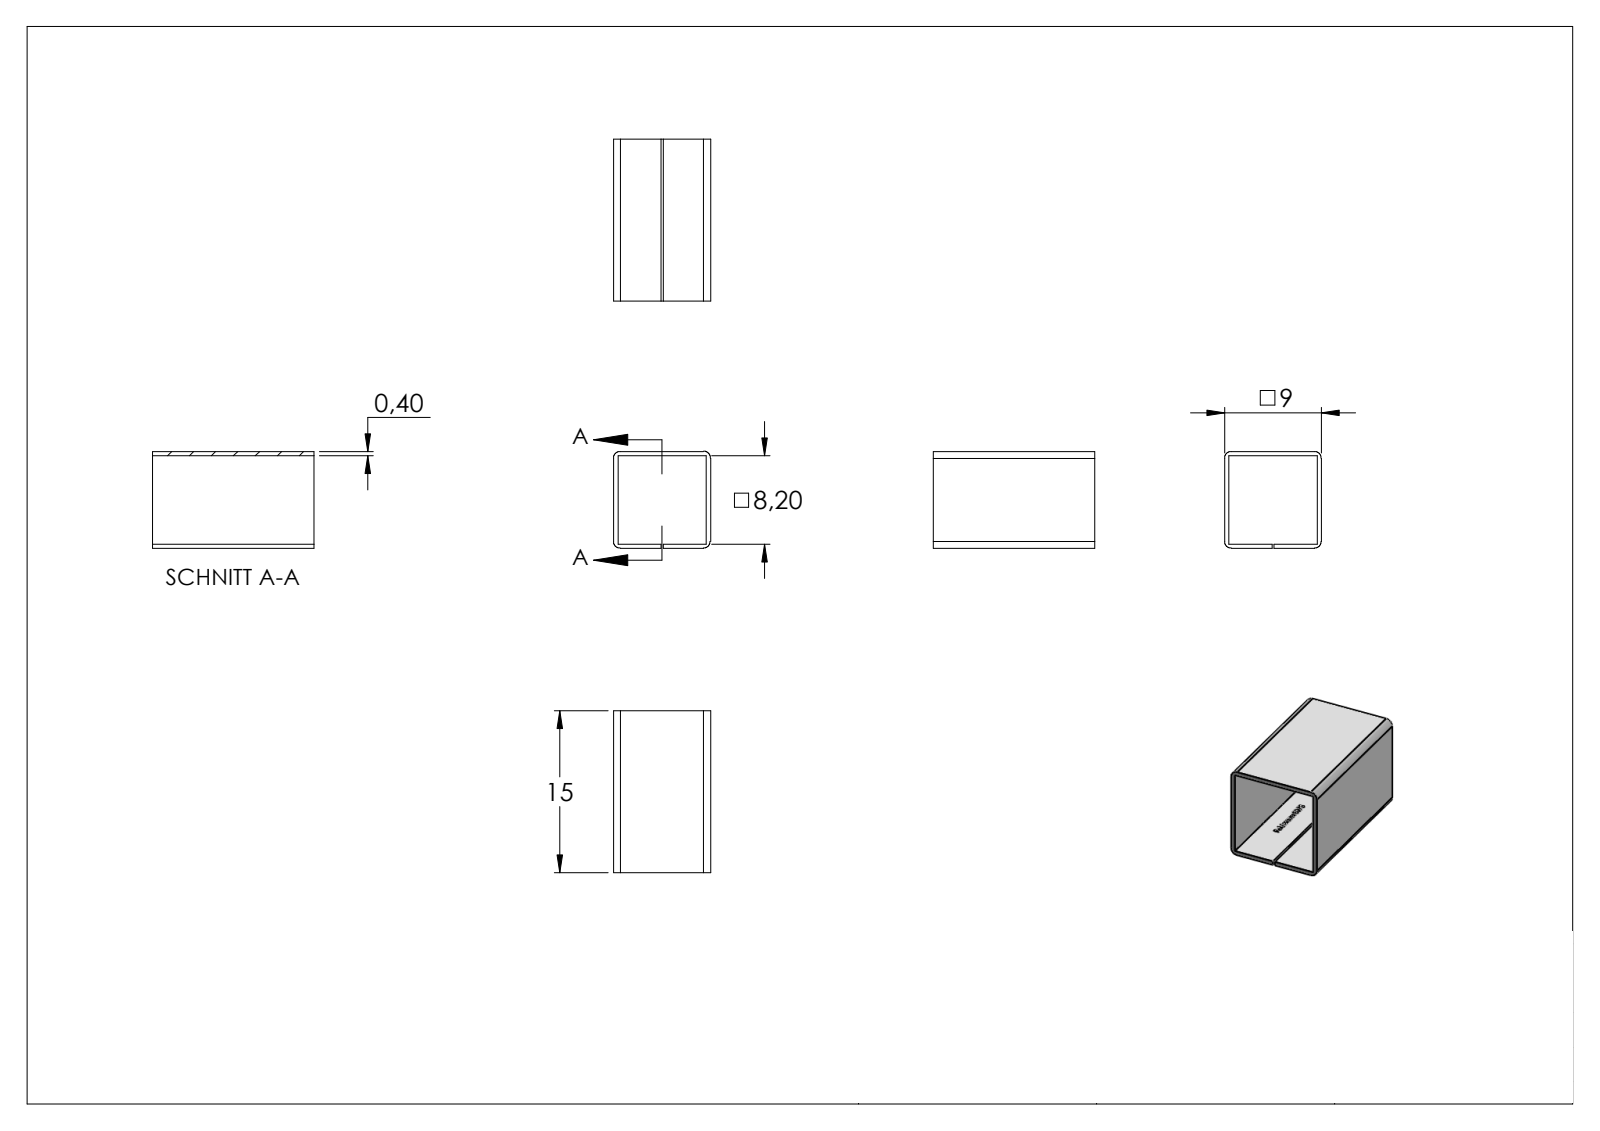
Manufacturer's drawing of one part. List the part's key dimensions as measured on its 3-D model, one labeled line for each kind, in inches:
Part name (STEP PRODUCT): 8073
STEP written by: SolidWorks 2018 (CONFIG_CONTROL_DESIGN)
Units: inches
Bodies: 1 solid, 187 faces (95 planar, 4 cylindrical, 88 other)
Overall size (bounding box): 0.591 × 0.354 × 0.354
Volume: 0.012 in³ · Surface area: 1.624 in²
Partial cylindrical surfaces — rounded edges, fillets, slot ends (radius × count): R0.026 ×4
Main face-to-face distances: 0.016, 0.339, 0.323, 0.354, 0.591, 0.173, 0.181, 0.157, 0.165, 0.015
